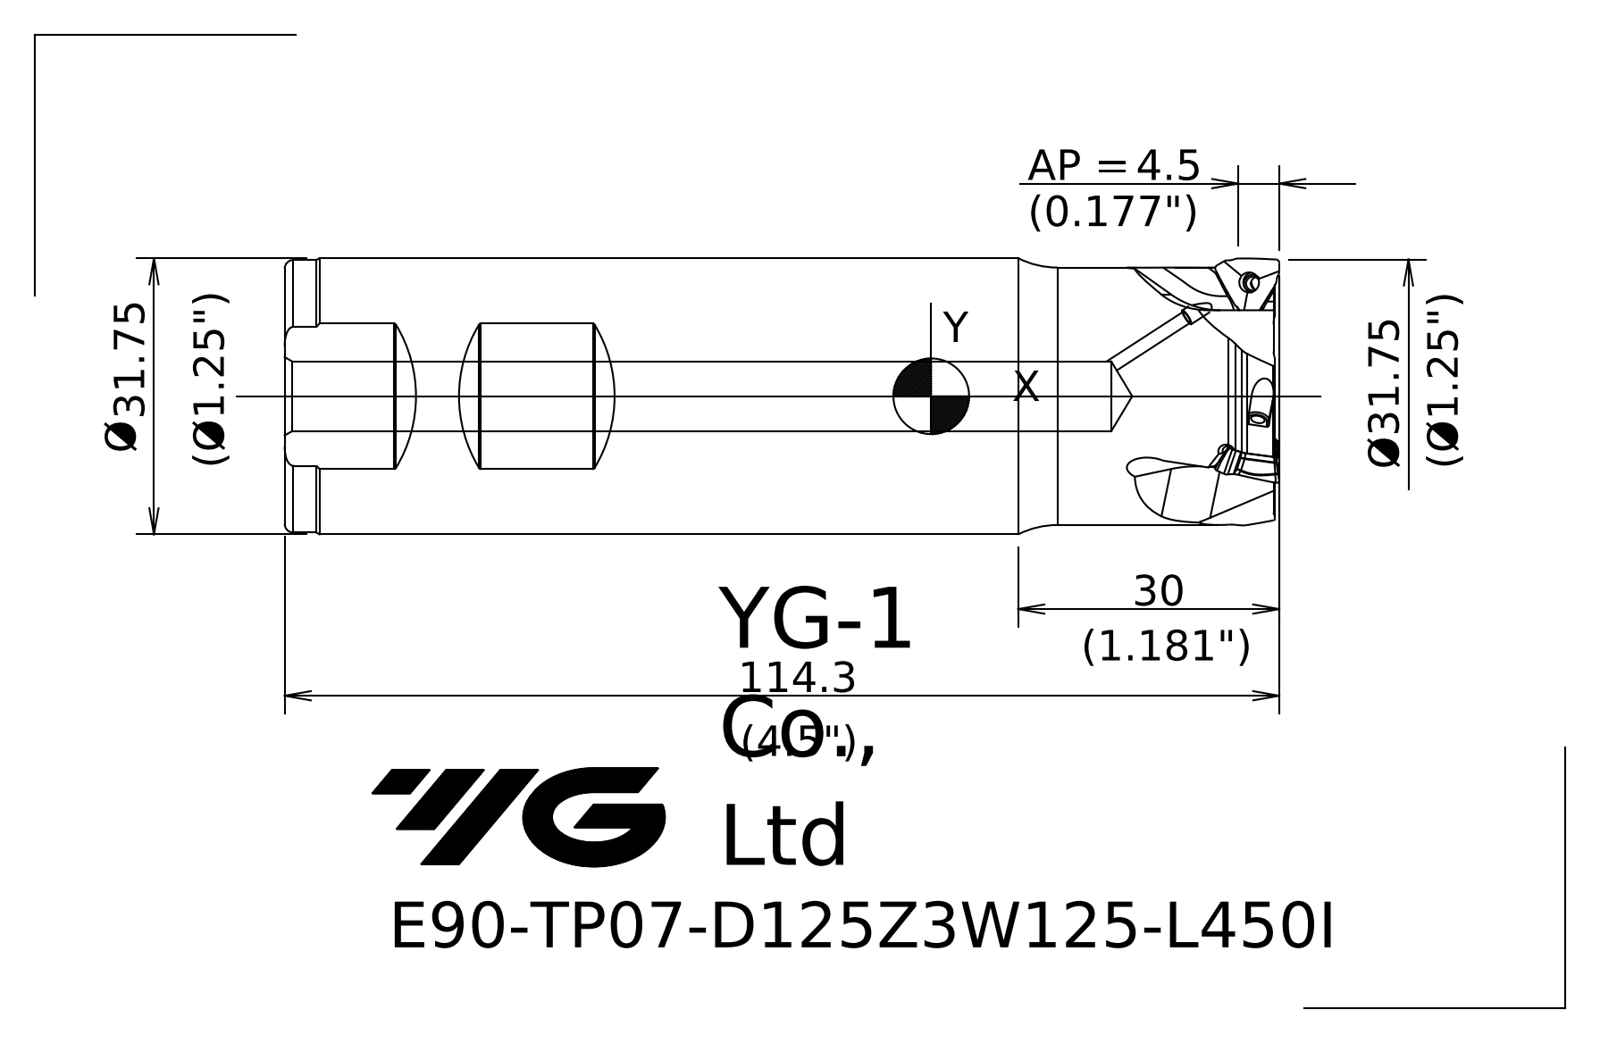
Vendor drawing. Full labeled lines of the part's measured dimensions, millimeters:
Part name (STEP PRODUCT): 10227044B04Ayxia
STEP written by: SIEMENS PLM Software NX 10.0 (AP203_CONFIGURATION_CONTROLLED_3D_DESIGN_OF_MECHANICAL_PARTS_AND_ASSEMBLIES_MIM_LF)
Units: millimetres
Bodies: 1 solid, 51 faces (8 planar, 8 cylindrical, 35 other)
Overall size (bounding box): 114.3 × 31.81 × 31.81
Volume: 81 530 mm³ · Surface area: 16 890 mm²
Round holes (diameter × count): ⌀1.5 ×1, ⌀8 ×1
Round bosses / shafts (diameter × count): ⌀31.75 ×1, ⌀31.35 ×1, ⌀29.6 ×1
Partial cylindrical surfaces — rounded edges, fillets, slot ends (radius × count): R0.3 ×3
Main face-to-face distances: 113.65, 113.8, 16.14
